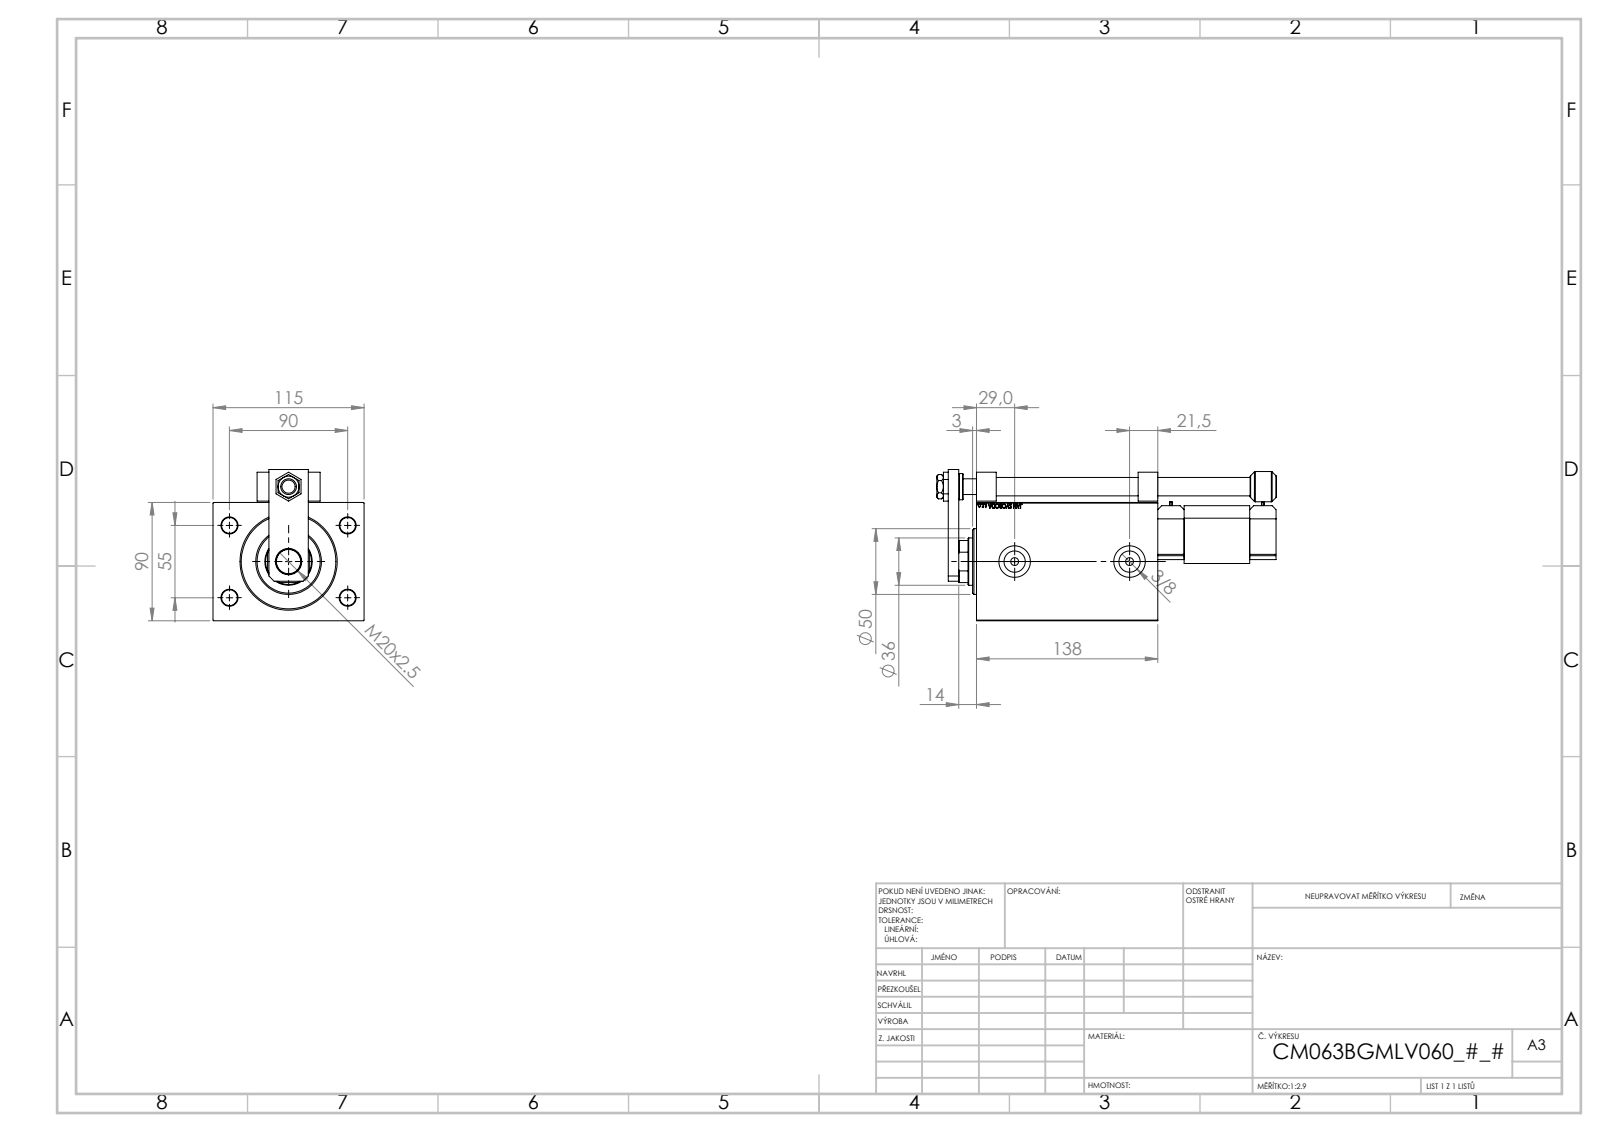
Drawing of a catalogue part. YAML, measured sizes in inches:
part_name: "SWITCH_P_FRONT_BACK; V450CM_B_VCP; KROUZEK_PRO_TYC; NUT_D16 (+7 more)"
step_written_by: "SolidWorks 2019 (CONFIG_CONTROL_DESIGN)"
units: inches
bodies: {solids: 14, faces: 1109, planar: 514, cylindrical: 114, other: 481}
overall_size: [10.177, 4.528, 4.528]
volume: 91.05
surface_area: 319.5
round_holes:
  - {diameter: 0.472, count: 5}
  - {diameter: 0.157, count: 4}
  - {diameter: 0.315, count: 4}
  - {diameter: 0.236, count: 2}
  - {diameter: 0.637, count: 2}
  - {diameter: 0.945, count: 2}
  - {diameter: 0.512, count: 1}
  - {diameter: 0.551, count: 1}
  - {diameter: 0.728, count: 1}
  - {diameter: 0.787, count: 1}
  - {diameter: 1.102, count: 1}
  - {diameter: 1.24, count: 1}
round_bosses_or_shafts:
  - {diameter: 0.787, count: 3}
  - {diameter: 0.63, count: 2}
  - {diameter: 0.551, count: 2}
  - {diameter: 0.236, count: 2}
  - {diameter: 1.969, count: 1}
  - {diameter: 0.906, count: 1}
partial_cylinders:
  - {radius: 0.118, count: 1}
  - {radius: 0.531, count: 1}
face_to_face_distances: [3.543, 4.528, 5.433, 1.476, 0.689, 4.744, 3.051, 0.787, 3.445, 2.756]
hole_center_spacings: [2.076, 0.787, 2.119, 2.165, 3.543, 3.769, 4.153, 4.843]
